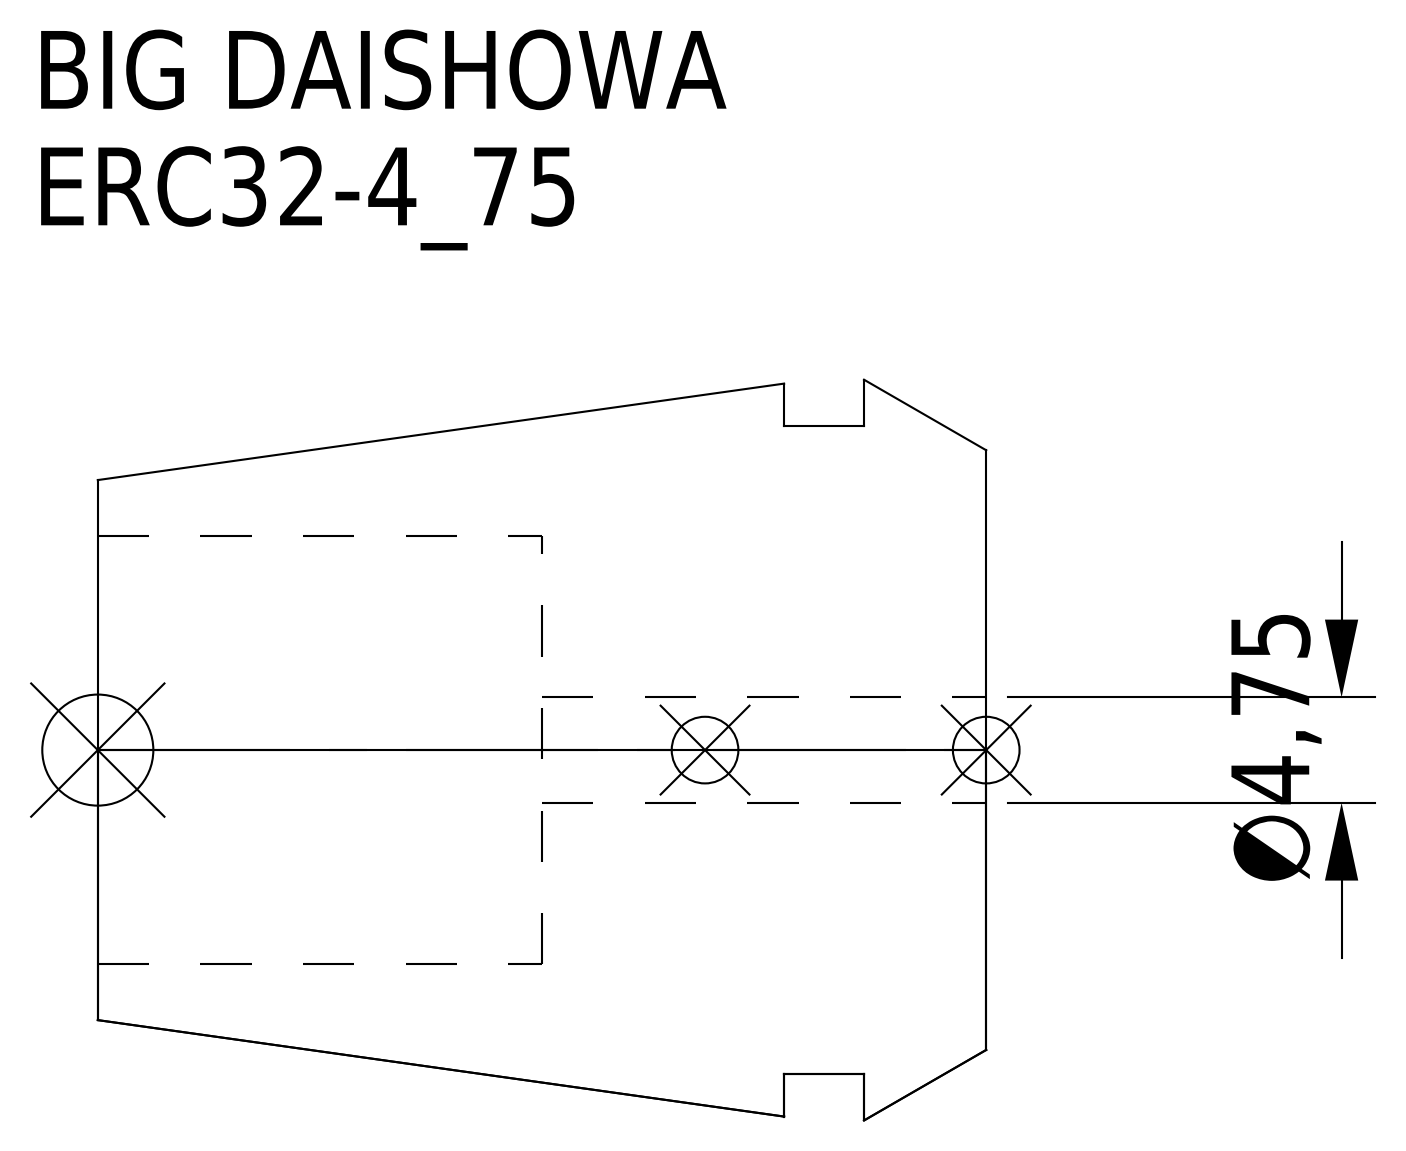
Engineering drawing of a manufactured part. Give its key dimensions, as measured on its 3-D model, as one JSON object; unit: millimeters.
{"part_name": "ERC32-4_75", "step_written_by": "CREO PARAMETRIC BY PTC INC, 2016380 (AUTOMOTIVE_DESIGN)", "units": "millimeters", "bodies": {"solids": 1, "faces": 15, "planar": 5, "cylindrical": 6, "other": 4}, "overall_size": [40, 33.35, 33.35], "volume_mm3": 20237, "surface_area_mm2": 6644, "round_holes": [[4.75, 1], [19.3, 1]], "round_bosses_or_shafts": [[29.2, 1]], "face_to_face_distances": [20, 5.5, 14.5, 9.1, 3.6, 10.9, 40, 34.5, 30.9]}
